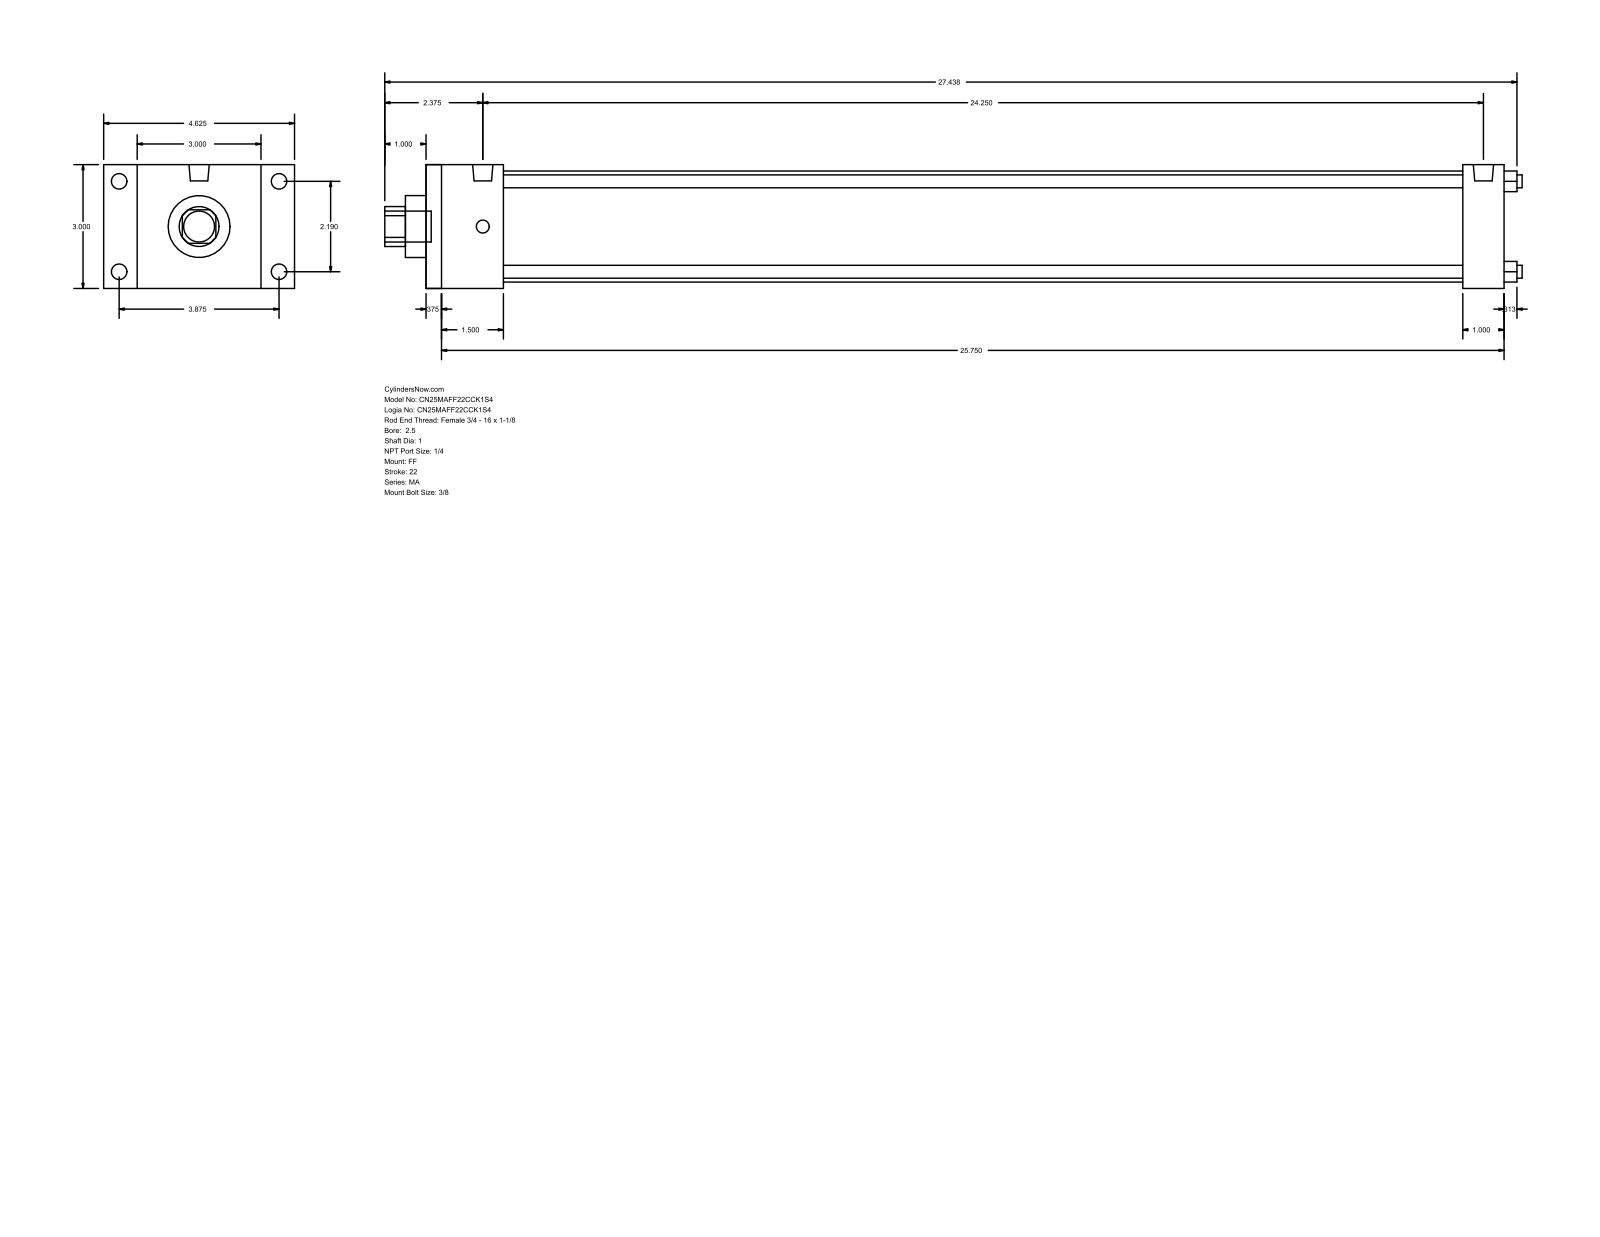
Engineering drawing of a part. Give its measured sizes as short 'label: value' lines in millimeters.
name: MA_FF__0250_1
written by: GSSL Pune (CONFIG_CONTROL_DESIGN)
unit: mm
bodies: 0 solids, 92 faces (64 planar, 28 cylindrical, 0 other)
size: 700.09 × 117.47 × 76.2
holes: 4× ⌀7.94, 1× ⌀25.4, 1× ⌀38.1, 1× ⌀68.33
bosses: 4× ⌀9.53, 4× ⌀7.94, 2× ⌀12.49, 1× ⌀19.05
rounds: 1× R12.29
face distances: 76.2, 663.58, 9.52, 654.06, 25.4, 47.63, 638.18, 38.11, 628.66, 590.55
hole spacings: 39.33, 55.62, 78.66
